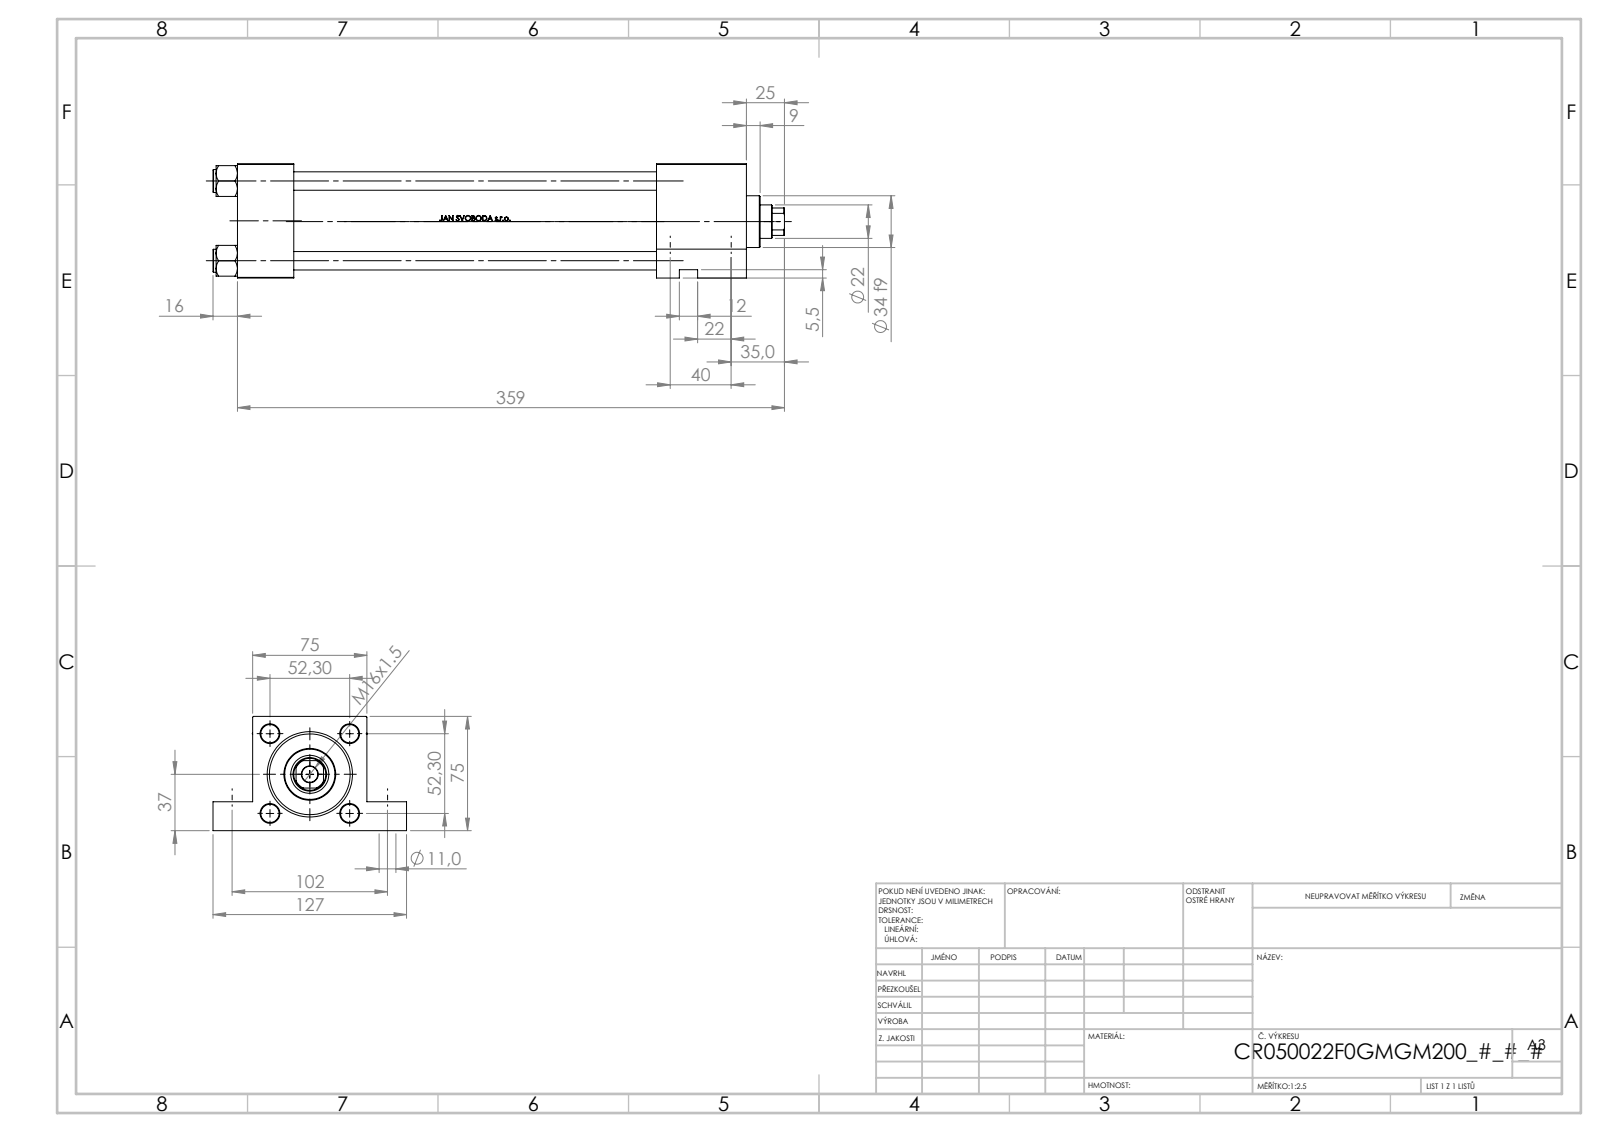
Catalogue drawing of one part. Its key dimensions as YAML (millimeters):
part_name: "V215CR_VCP_F; V215_VC_A; V215CR_F_TYCINKA; NUT_M5_F (+1 more)"
step_written_by: "SolidWorks 2019 (CONFIG_CONTROL_DESIGN)"
units: millimeters
bodies: {solids: 11, faces: 1103, planar: 437, cylindrical: 126, other: 540}
overall_size: [375, 127, 75]
volume: 946468
surface_area: 255877
round_holes:
  - {diameter: 11, count: 4}
  - {diameter: 12, count: 4}
  - {diameter: 7, count: 2}
  - {diameter: 30, count: 2}
  - {diameter: 10.5, count: 1}
  - {diameter: 17, count: 1}
  - {diameter: 20.96, count: 1}
  - {diameter: 22, count: 1}
  - {diameter: 25, count: 1}
  - {diameter: 41, count: 1}
  - {diameter: 50, count: 1}
  - {diameter: 53, count: 1}
round_bosses_or_shafts:
  - {diameter: 15, count: 4}
  - {diameter: 56, count: 1}
  - {diameter: 34, count: 1}
partial_cylinders:
  - {radius: 10.5, count: 1}
face_to_face_distances: [75, 37, 297, 334, 275, 238, 59, 305.3, 268.3, 30.3]
hole_center_spacings: [52.3, 36.63, 37.34, 40, 73.96, 102, 109.56, 273.5]
